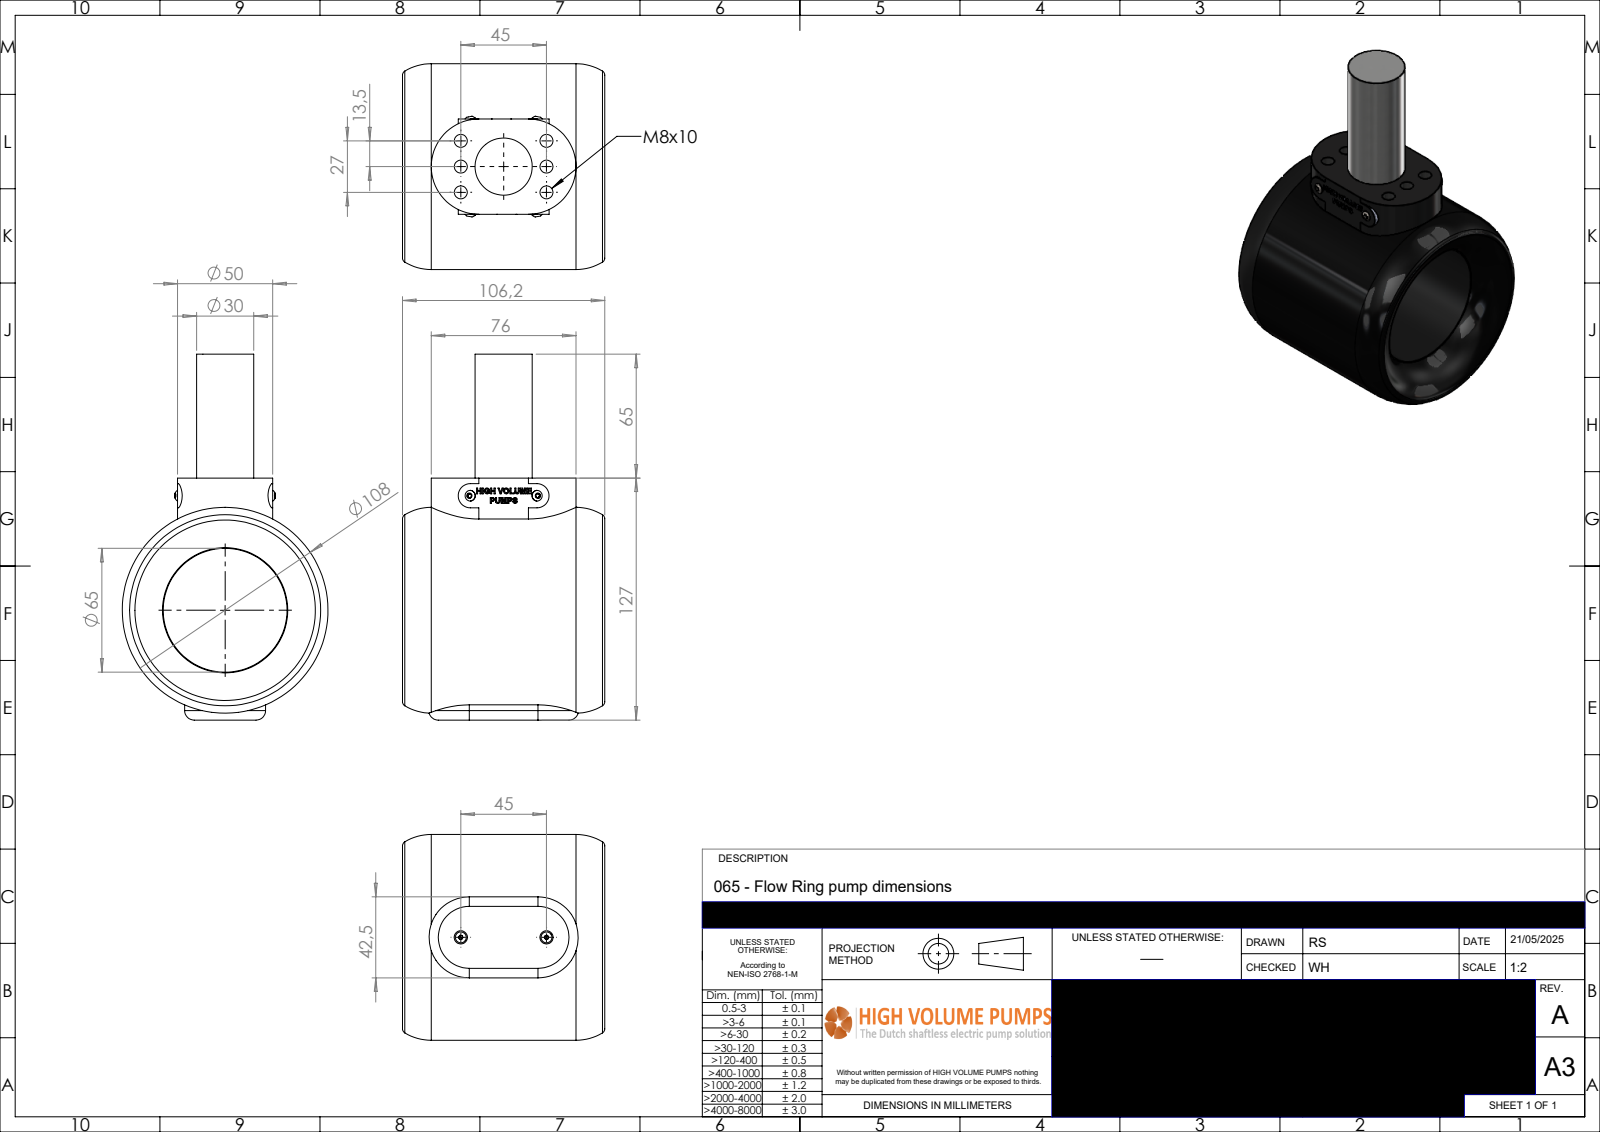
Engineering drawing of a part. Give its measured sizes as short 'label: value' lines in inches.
name: P-065-030-rev-A-FR
written by: SolidWorks 2024 (AUTOMOTIVE_DESIGN)
unit: in
bodies: 1 solid, 561 faces (379 planar, 38 cylindrical, 144 other)
size: 7.559 × 4.252 × 4.18
volume: 41.74 in³; area: 118 in²
holes: 6× ⌀0.268, 2× ⌀0.138, 1× ⌀2.559, 1× ⌀4.252
bosses: 4× ⌀0.118, 2× ⌀0.224, 1× ⌀1.181
rounds: 4× R0.112, 2× R0.197, 2× R0.25, 2× R0.837, 2× R0.984
face distances: 5, 7.559, 2.559, 1.969, 0.148, 4.646, 0.354, 2.913, 1.821, 1.965
hole spacings: 0.531, 1.85, 1.772, 1.063, 2.066, 1.378
